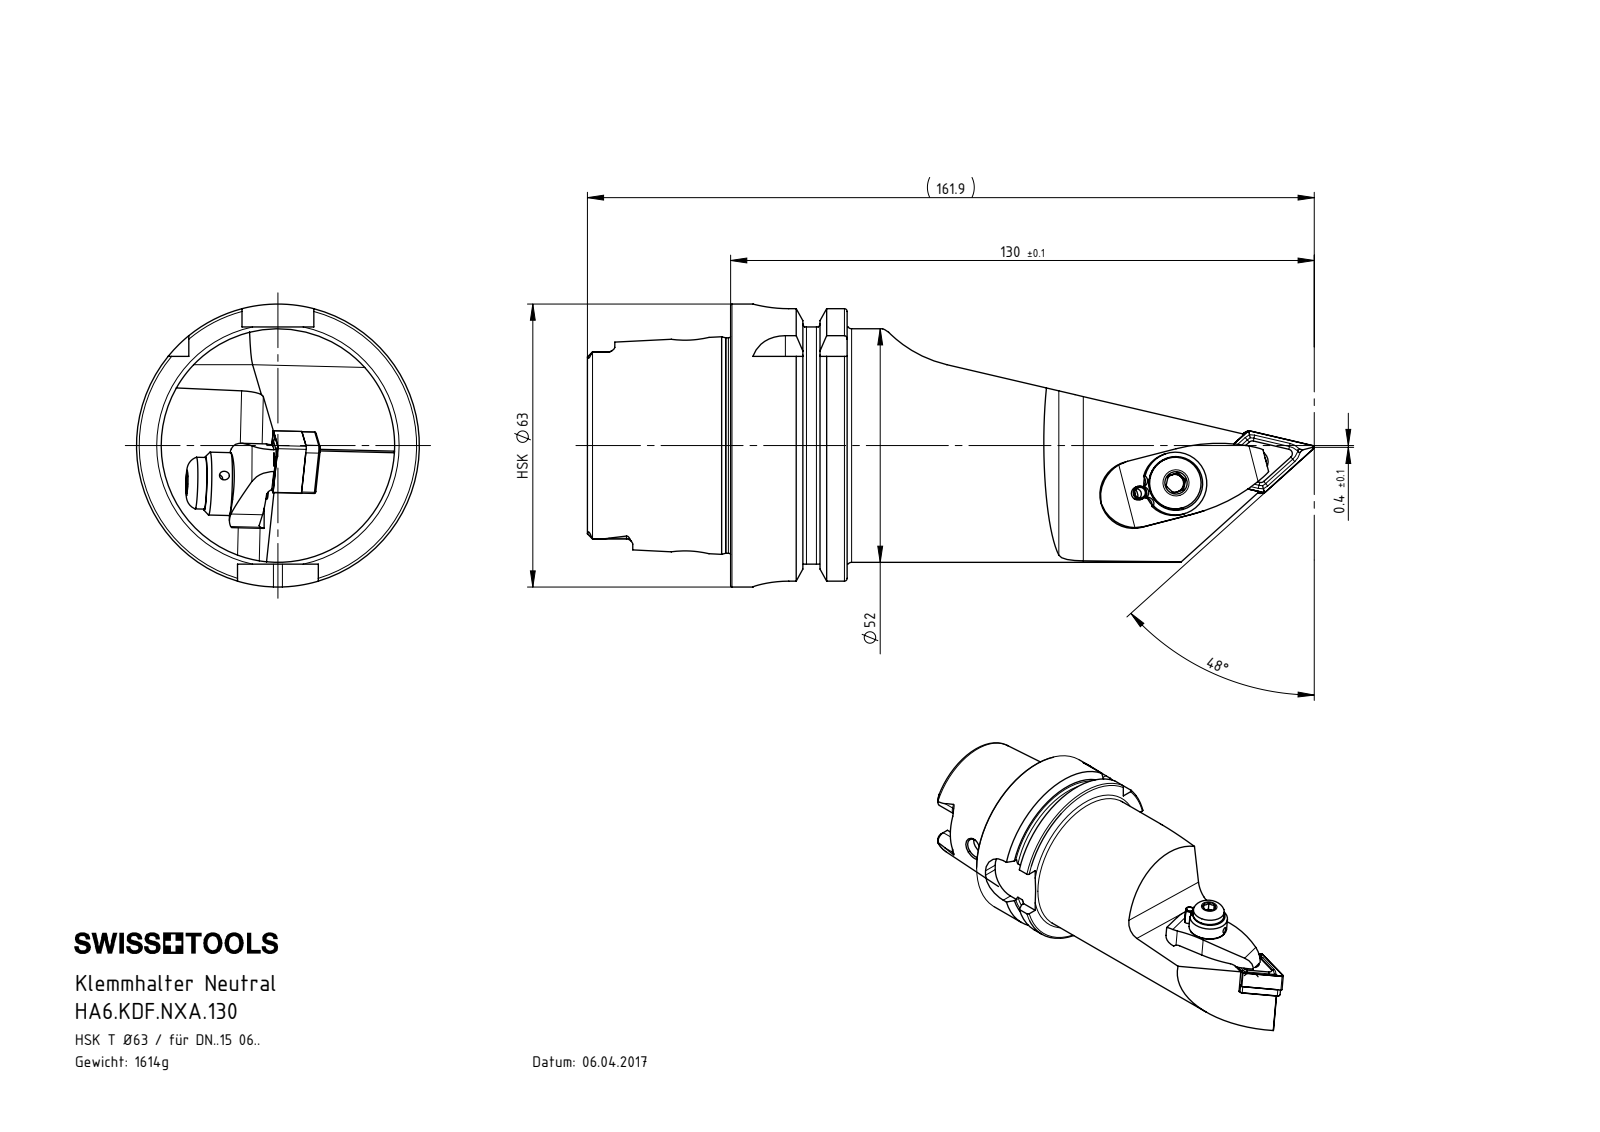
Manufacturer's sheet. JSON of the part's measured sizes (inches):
{"part_name": "HA6-KDF.NXA.130; ISO 13337 - 3 x 12_PreviewCfg; KVT_MB_600_050; WCC-ER5.102.012_C (+7 more)", "step_written_by": "SolidWorks 2017 (CONFIG_CONTROL_DESIGN)", "units": "inches", "bodies": {"solids": 11, "faces": 470, "planar": 125, "cylindrical": 156, "other": 189}, "overall_size": [6.374, 2.48, 2.48], "volume_in3": 12.66, "surface_area_in2": 64.32, "round_holes": [[0.079, 3], [0.197, 3], [0.157, 2], [0.165, 2], [0.244, 2], [0.276, 2], [0.094, 1], [0.118, 1], [0.203, 1], [0.252, 1], [0.295, 1], [0.331, 1]], "round_bosses_or_shafts": [[0.197, 2], [0.118, 2], [2.48, 1], [2.163, 1], [2.047, 1], [1.887, 1], [0.551, 1], [0.453, 1]], "partial_cylinders_radius": [[0.015, 6], [0.055, 6], [0.016, 4], [0.039, 4], [0.315, 4], [0.027, 3], [0.027, 3], [0.059, 3]], "face_to_face_distances": [1.022, 0.63, 0.392, 0.238, 1.256, 1.648, 2.278, 2.079, 0.125, 0.363], "hole_center_spacings": [0.313, 0.323, 0.778, 0.787, 0.323, 1.101, 1.101]}
